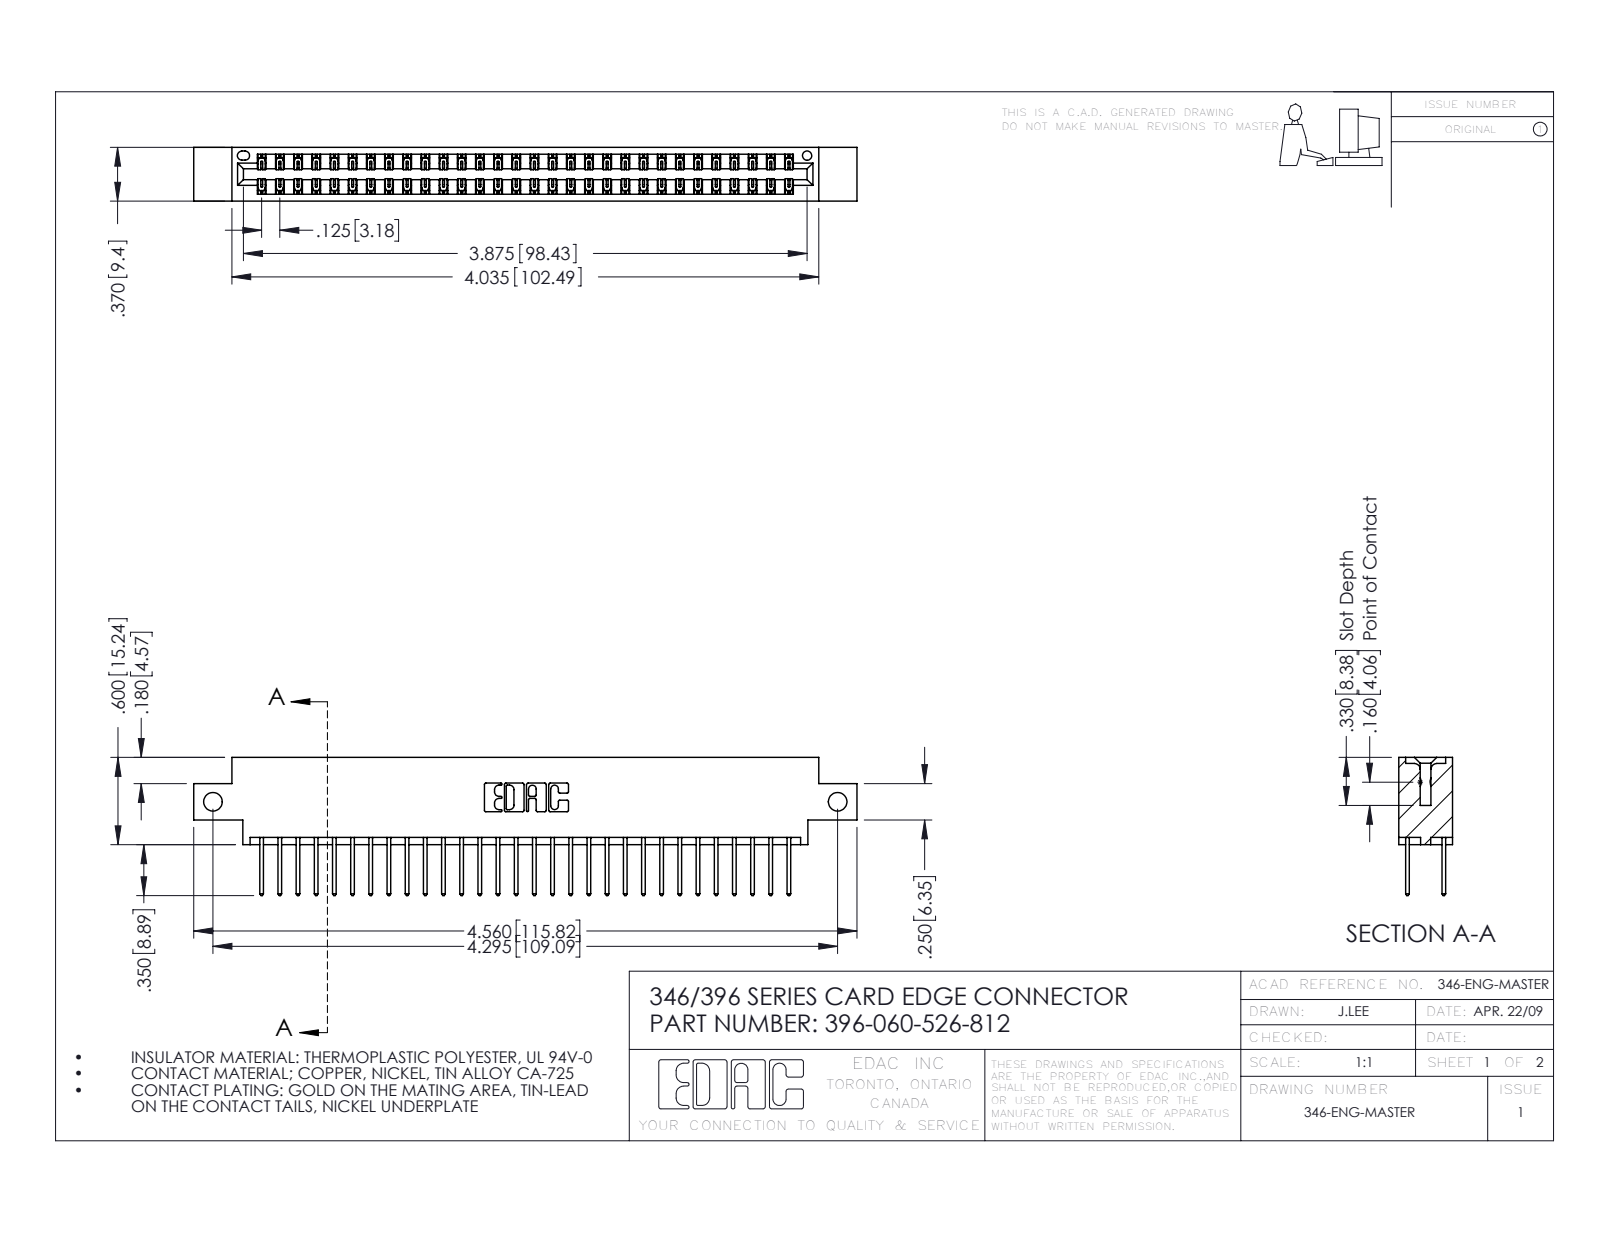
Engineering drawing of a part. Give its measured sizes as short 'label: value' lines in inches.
name: 396-060-526-812; 346 Part_0.170 Offset - Side Mount; 345-292-001_345-293-126
written by: SolidWorks 2016 (CONFIG_CONTROL_DESIGN)
unit: in
bodies: 61 solids, 3246 faces (2180 planar, 1066 cylindrical, 0 other)
size: 4.56 × 0.95 × 0.37
volume: 0.675 in³; area: 24.01 in²
holes: 2× ⌀0.128, 1× ⌀0.064
rounds: 90× R0.006, 60× R0.01, 22× R0.01, 6× R0.007, 6× R0.031, 3× R0.026, 2× R0.014, 2× R0.022
face distances: 0.048, 0.322, 0.25, 0.37, 0.072, 0.298, 0.025, 0.275, 0.148, 0.222
hole spacings: 4.295
